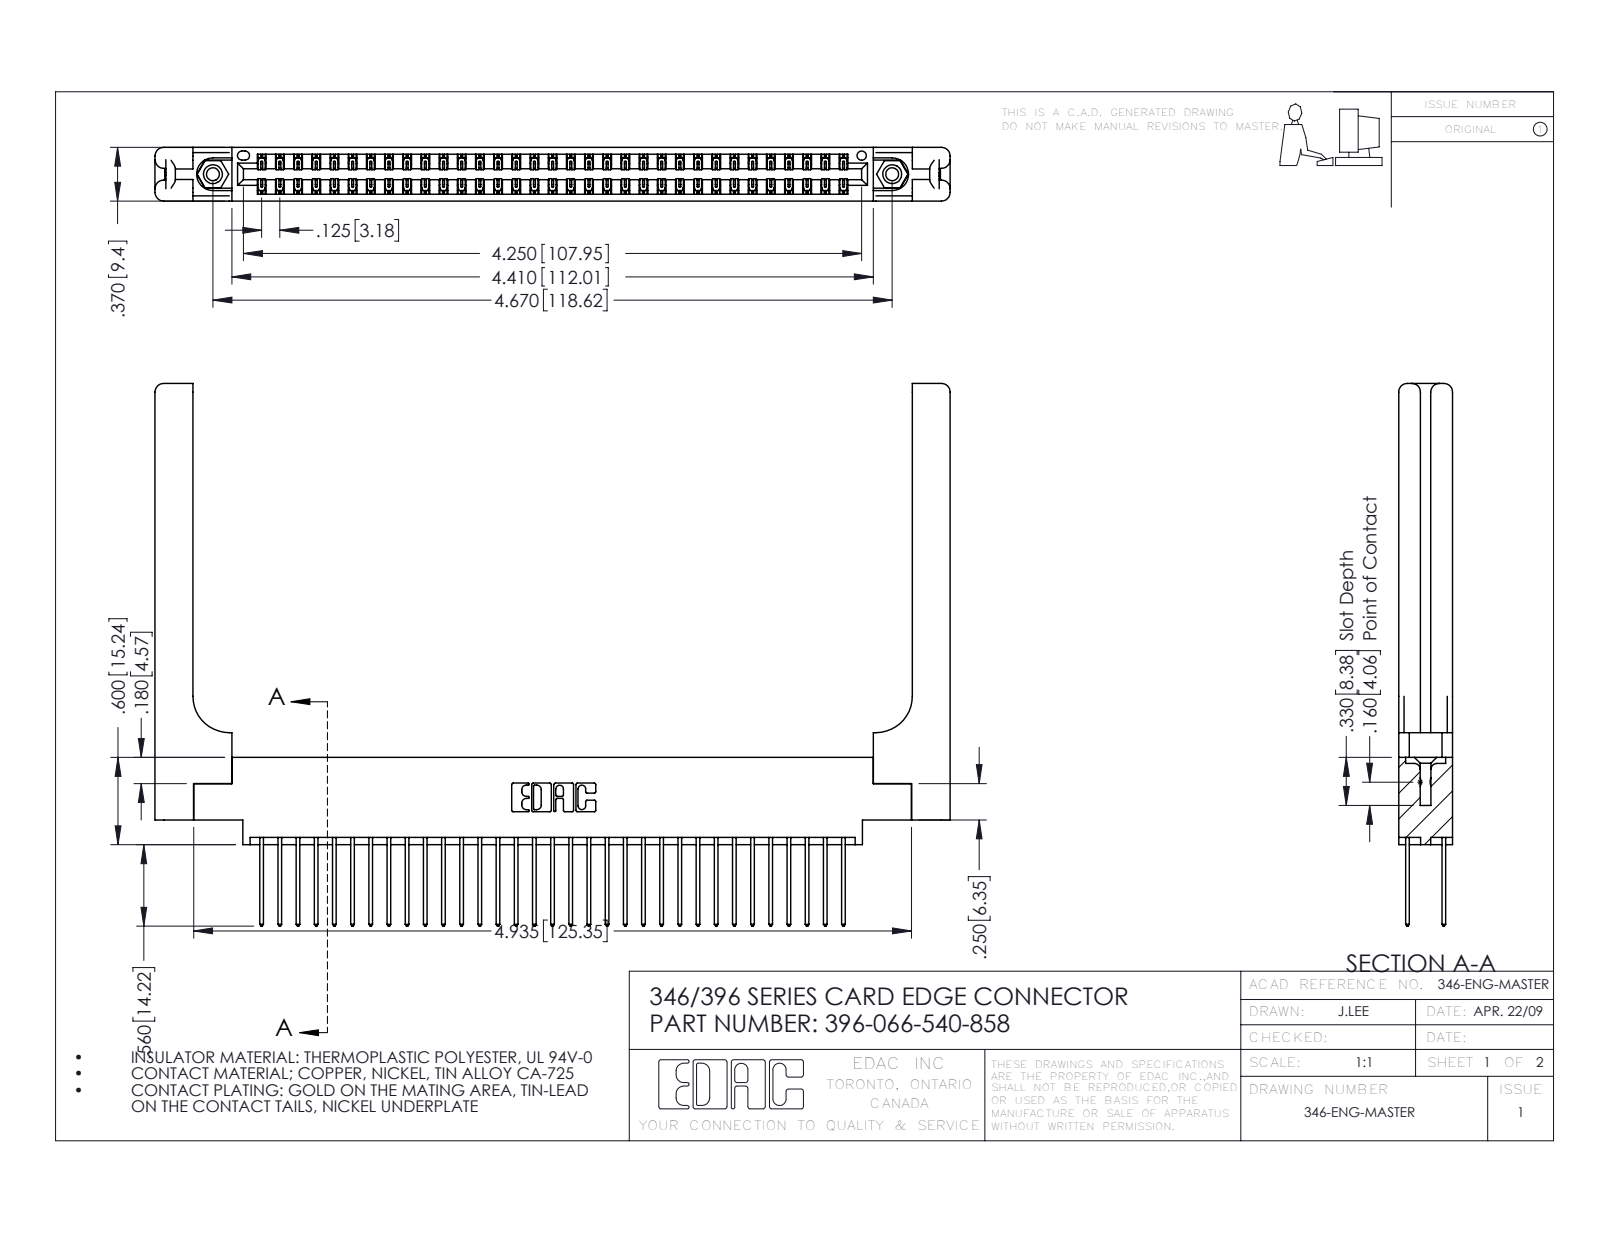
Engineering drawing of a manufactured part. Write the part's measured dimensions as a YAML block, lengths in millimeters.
part_name: "396-066-540-858; 346-220-058_345-220-058; 346 Part_0.170 Offset - 0.156 Dia-TH; 345-250-001_345-250-001-102 (+1 more)"
step_written_by: "SolidWorks 2016 (CONFIG_CONTROL_DESIGN)"
units: millimeters
bodies: {solids: 71, faces: 3814, planar: 2538, cylindrical: 1216, other: 60}
overall_size: [138.8, 94.7, 9.4]
volume: 21060
surface_area: 24840
round_holes:
  - {diameter: 2.3, count: 2}
  - {diameter: 3.2, count: 2}
  - {diameter: 4, count: 2}
  - {diameter: 1.6, count: 1}
round_bosses_or_shafts:
  - {diameter: 3.9, count: 2}
partial_cylinders:
  - {radius: 0.2, count: 99}
  - {radius: 0.3, count: 66}
  - {radius: 0.3, count: 22}
  - {radius: 1.5, count: 16}
  - {radius: 0.2, count: 6}
  - {radius: 0.8, count: 6}
  - {radius: 0.7, count: 3}
  - {radius: 0.4, count: 2}
face_to_face_distances: [1.2, 8.2, 9.4, 1.8, 6.4, 0.6, 7.6, 3.8, 3.8, 7]
hole_center_spacings: [6.2, 113.3, 118.6]
